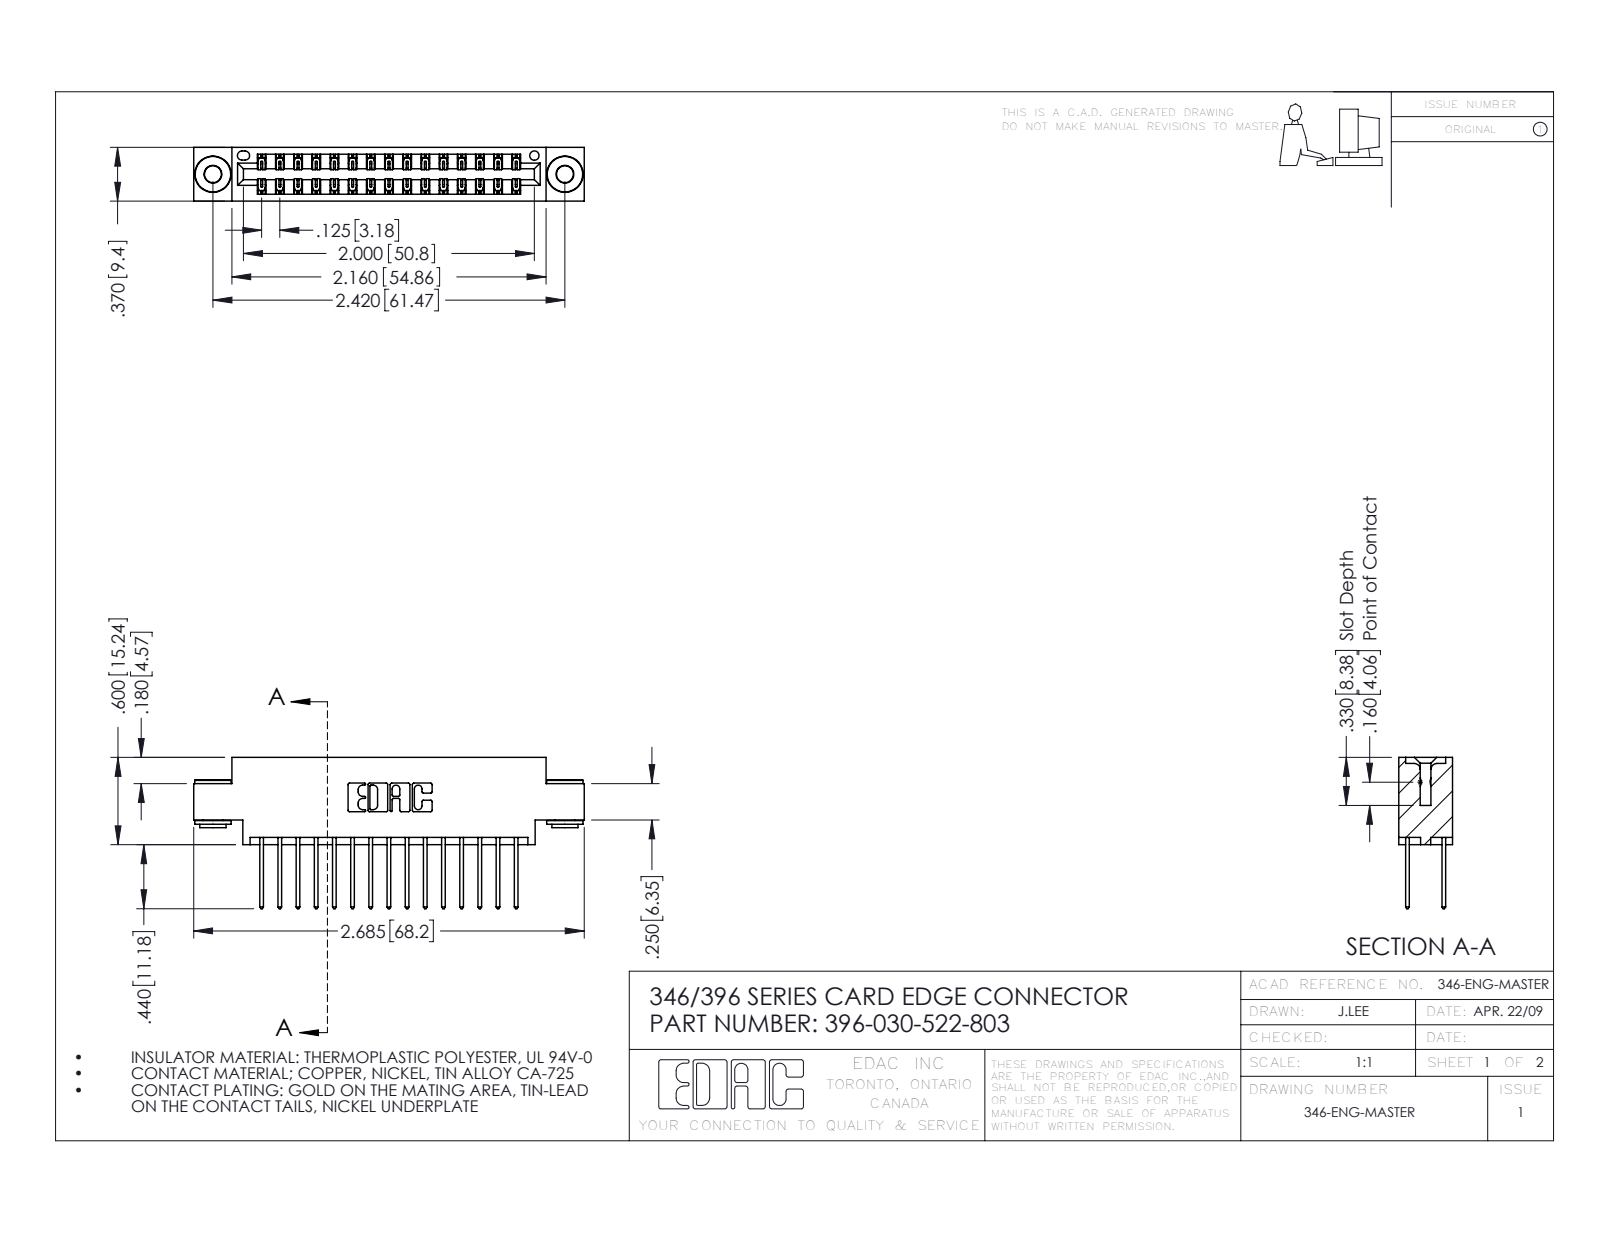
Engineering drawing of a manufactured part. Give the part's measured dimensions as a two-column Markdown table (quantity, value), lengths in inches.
| quantity | value |
| --- | --- |
| part name | 346 Part_0.170 Offset - 0.156 Dia-TH; 345-292-001_345-293-122; 345-250-002_345-250-002-102; 396-030-522-803 |
| STEP written by | SolidWorks 2016 (CONFIG_CONTROL_DESIGN) |
| units | inches |
| bodies | 33 solids, 1724 faces (1140 planar, 576 cylindrical, 8 other) |
| overall size | 2.685 × 1.04 × 0.37 |
| volume | 0.389 in³ |
| surface area | 14.1 in² |
| round holes (diameter × count) | 0.116 × 2, 0.156 × 2, 0.064 × 1 |
| round bosses / shafts (diameter × count) | 0.25 × 2, 0.18 × 2, 0.136 × 2 |
| partial cylindrical surfaces (radius × count) | 0.006 × 45, 0.01 × 30, 0.01 × 22, 0.007 × 6, 0.031 × 6, 0.026 × 3, 0.014 × 2, 0.022 × 2 |
| main face-to-face distances | 0.048, 0.322, 0.25, 0.37, 0.025, 0.072, 0.298, 0.275, 0.148, 0.222 |
| hole center spacings | 0.246, 2.213, 2.42 |
